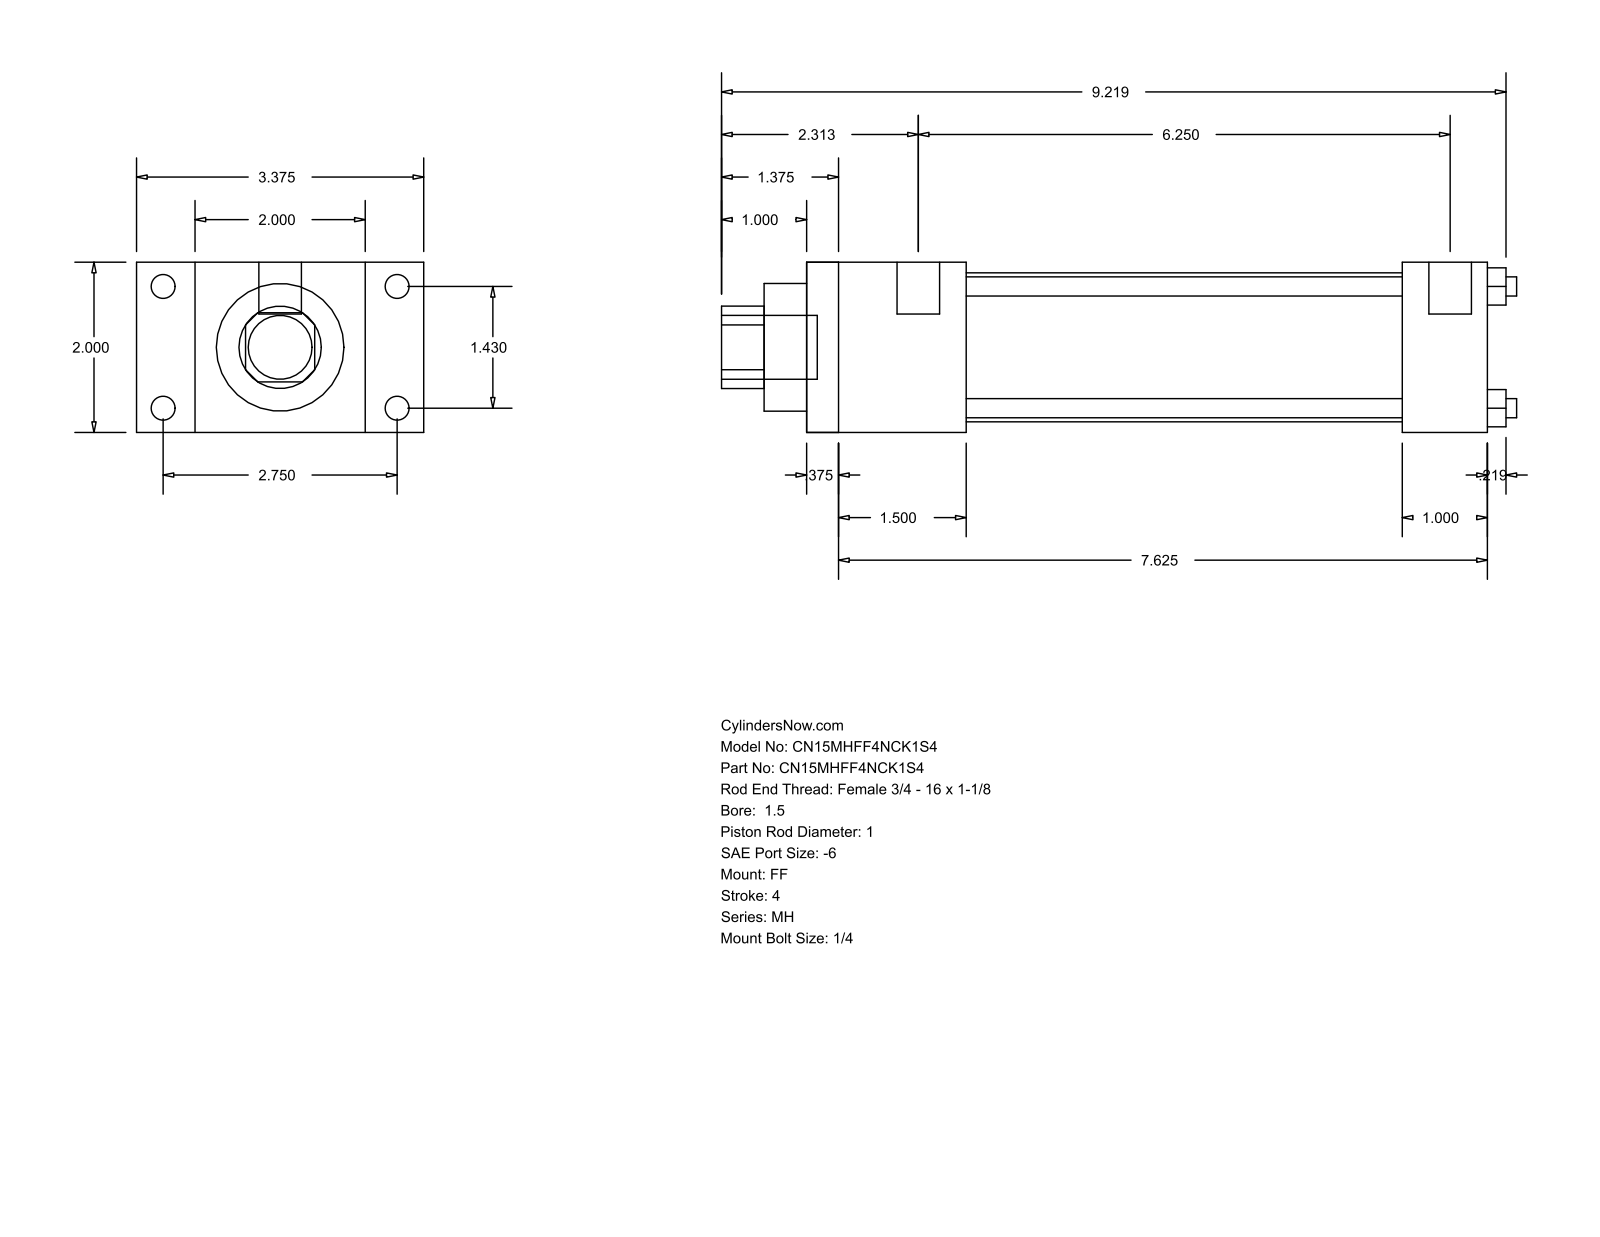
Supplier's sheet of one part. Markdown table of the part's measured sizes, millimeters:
| quantity | value |
| --- | --- |
| part name | MH_FF__0150_1 |
| STEP written by | GSSL Pune (CONFIG_CONTROL_DESIGN) |
| units | millimeters |
| bodies | 0 solids, 92 faces (64 planar, 28 cylindrical, 0 other) |
| overall size | 237.33 × 85.72 × 50.8 |
| round holes (diameter × count) | 5.71 × 4, 25.4 × 1, 38.1 × 1, 44.45 × 1 |
| round bosses / shafts (diameter × count) | 7.14 × 4, 5.56 × 4, 12.7 × 2, 19.05 × 1 |
| partial cylindrical surfaces (radius × count) | 12.29 × 1 |
| main face-to-face distances | 50.8, 203.2, 9.52, 193.68, 25.4, 17.46, 68.26, 47.63, 38.11, 155.57 |
| hole center spacings | 25.68, 36.32, 51.36 |
